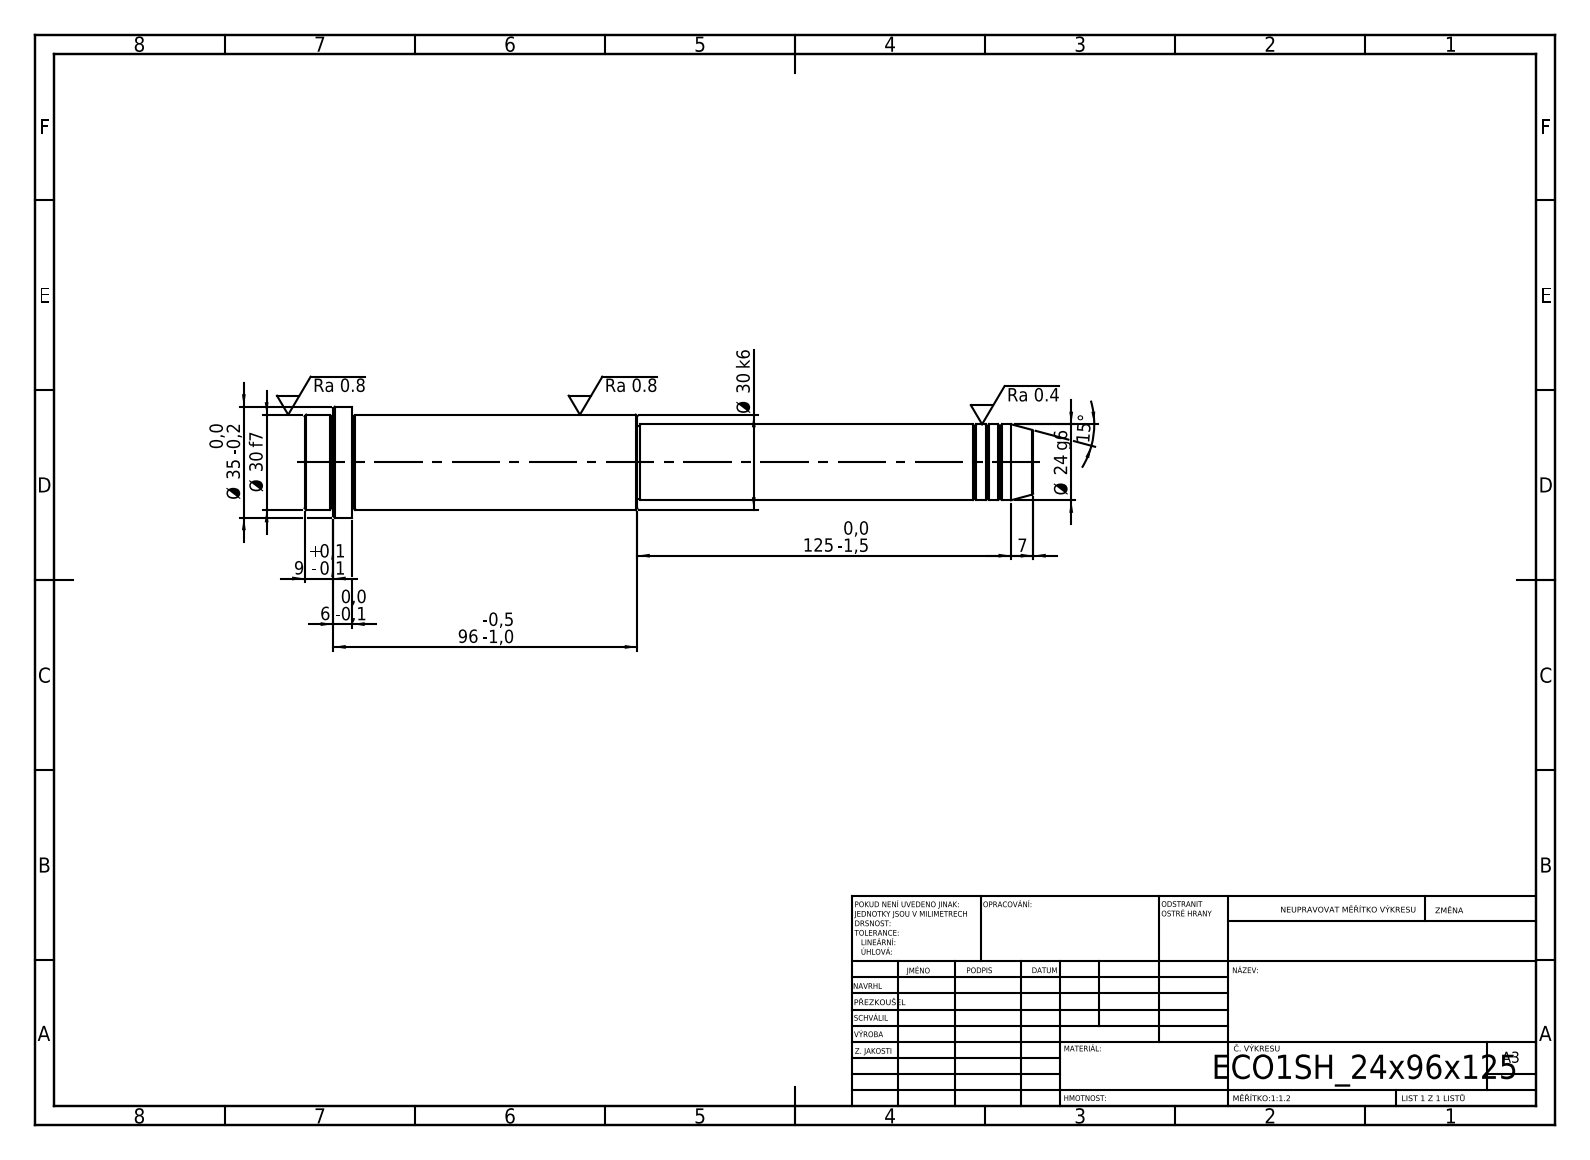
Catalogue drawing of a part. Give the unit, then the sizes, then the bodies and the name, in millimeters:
Units: millimetres
Overall size (bounding box): 230 × 35 × 35
Round bosses / shafts (diameter × count): ⌀35 ×1, ⌀30 ×1, ⌀24 ×1, ⌀23 ×1
Main face-to-face distances: 230, 215, 15, 125, 90, 105, 221, 96, 6, 9
Volume: 131 595 mm³ · Surface area: 21 381 mm²
Bodies: 1 solid, 52 faces (6 planar, 16 cylindrical, 30 other)
STEP written by: SolidWorks 2019 (CONFIG_CONTROL_DESIGN)
